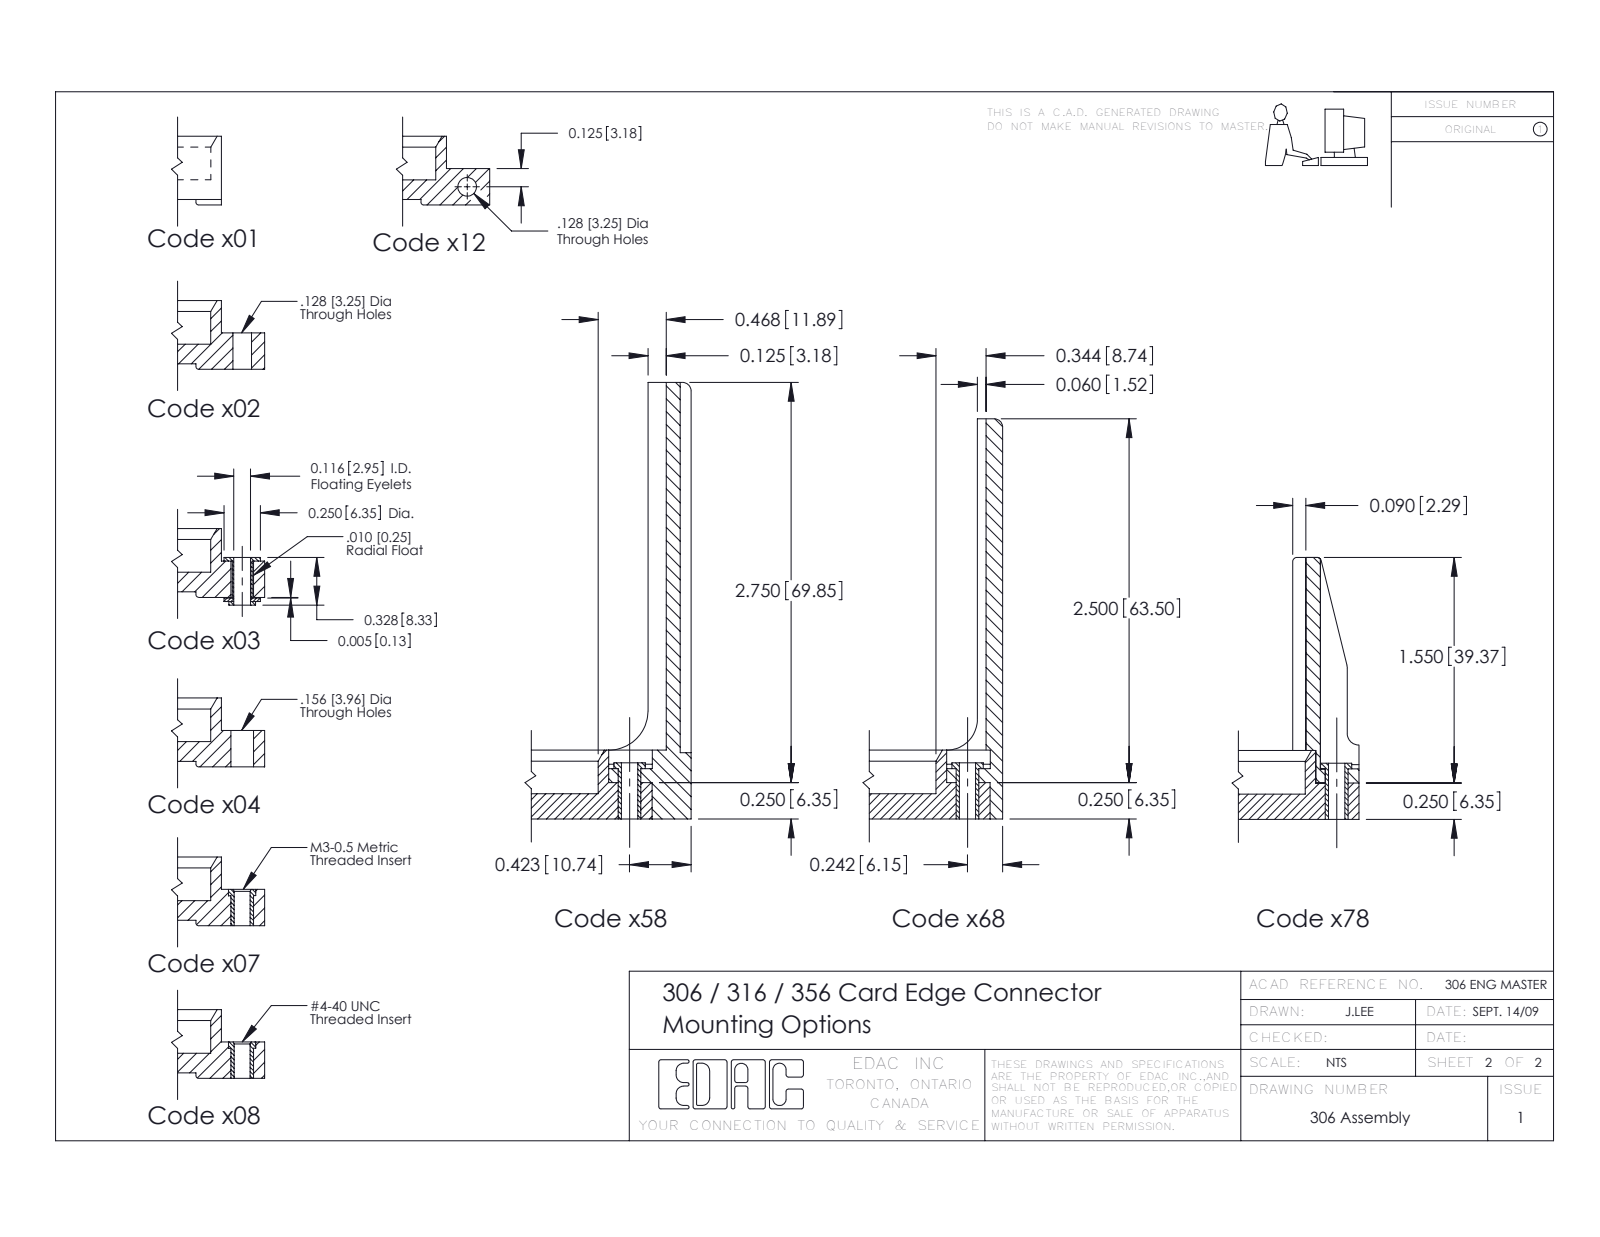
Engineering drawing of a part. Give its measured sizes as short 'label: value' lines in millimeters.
name: 306-006-500-101; 306-290-001_100; 306 Part_No Mounting
written by: SolidWorks 2016 (CONFIG_CONTROL_DESIGN)
unit: mm
bodies: 7 solids, 564 faces (364 planar, 176 cylindrical, 24 other)
size: 31.6 × 18.9 × 8.7
volume: 2 390 mm³; area: 3 386 mm²
rounds: 23× R0.4, 22× R0.3, 12× R0.6, 12× R0.8, 6× R0.2, 6× R0.8, 3× R0.7, 2× R1.7
face distances: 8.7, 2.1, 6.6, 0.4, 4, 0.8, 1.1, 1.5, 4.6, 10.9
